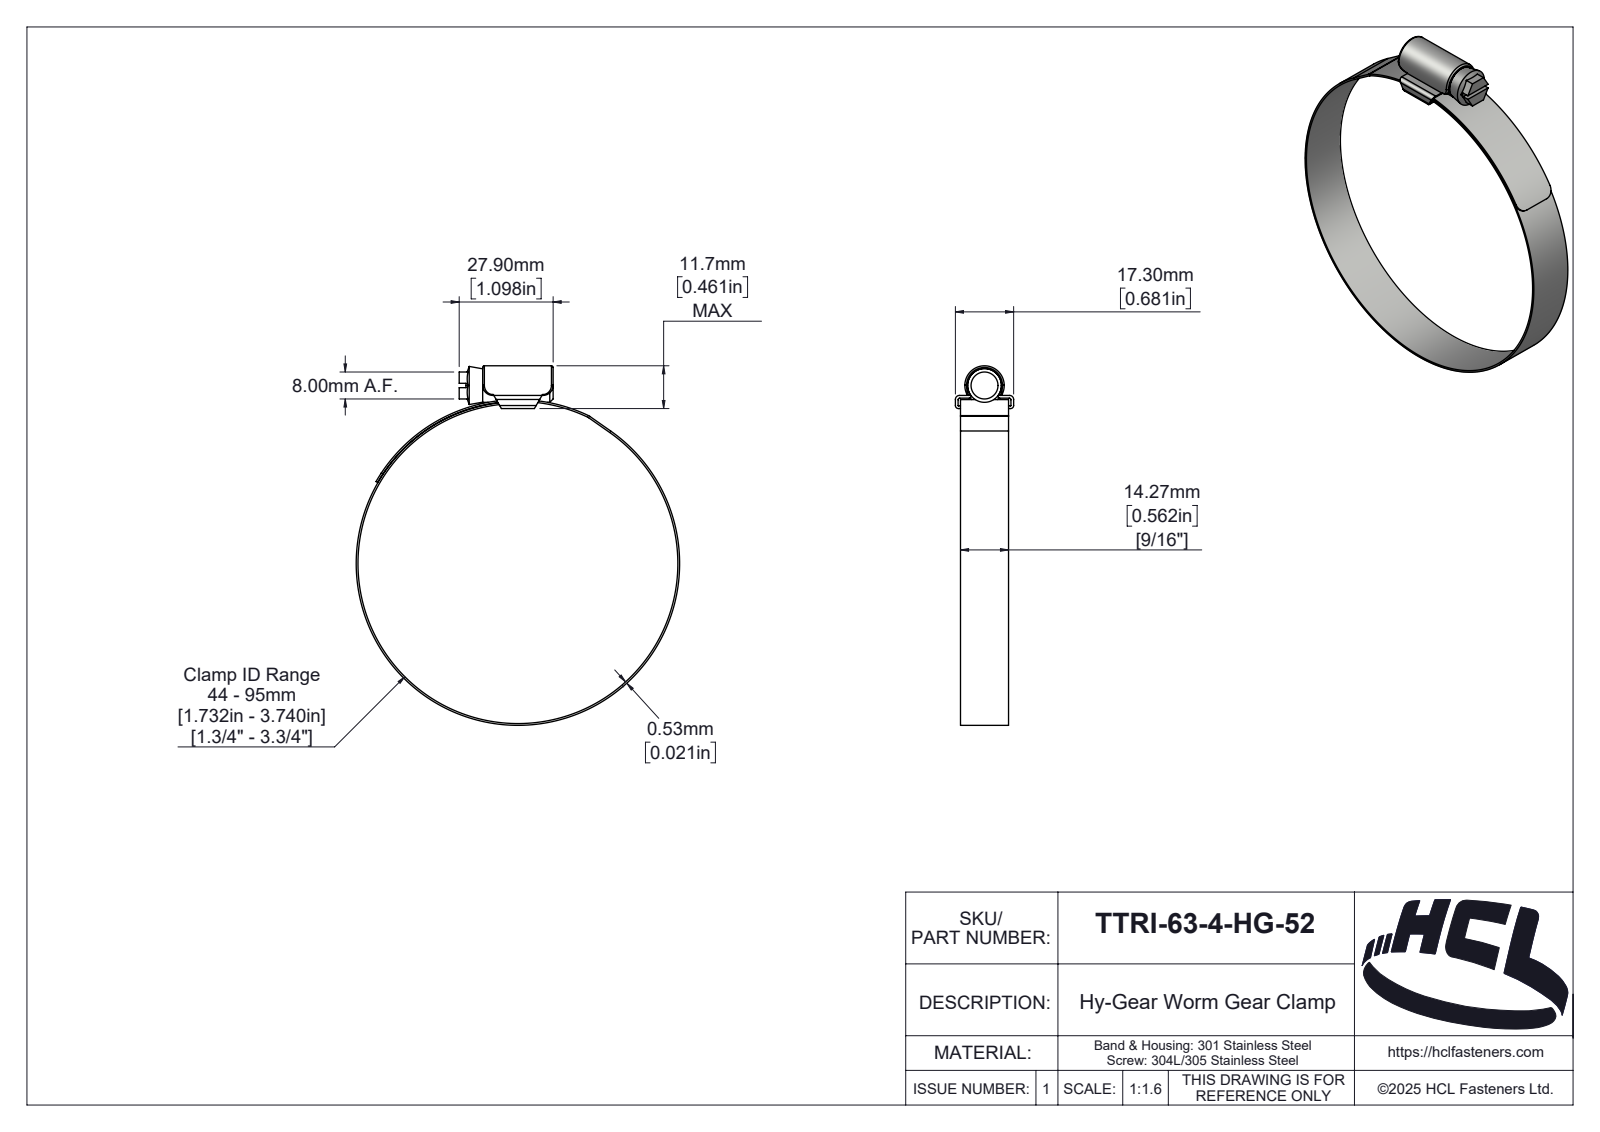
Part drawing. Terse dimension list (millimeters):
name: TRI-50-0-HG-52
written by: SolidWorks 2025 (AUTOMOTIVE_DESIGN)
unit: mm
bodies: 3 solids, 189 faces (39 planar, 89 cylindrical, 61 other)
size: 106.73 × 96.06 × 17.3
volume: 5 446 mm³; area: 13 193 mm²
holes: 1× ⌀95
bosses: 1× ⌀96.06, 1× ⌀10
rounds: 6× R0.5, 4× R3, 2× R0.1, 2× R0.9, 2× R1.2, 1× R0.46, 1× R1.89, 1× R2
face distances: 0.8, 14.26, 3.1, 0.53, 2.3, 3.9, 27.9, 1.52, 15.78, 16.5
